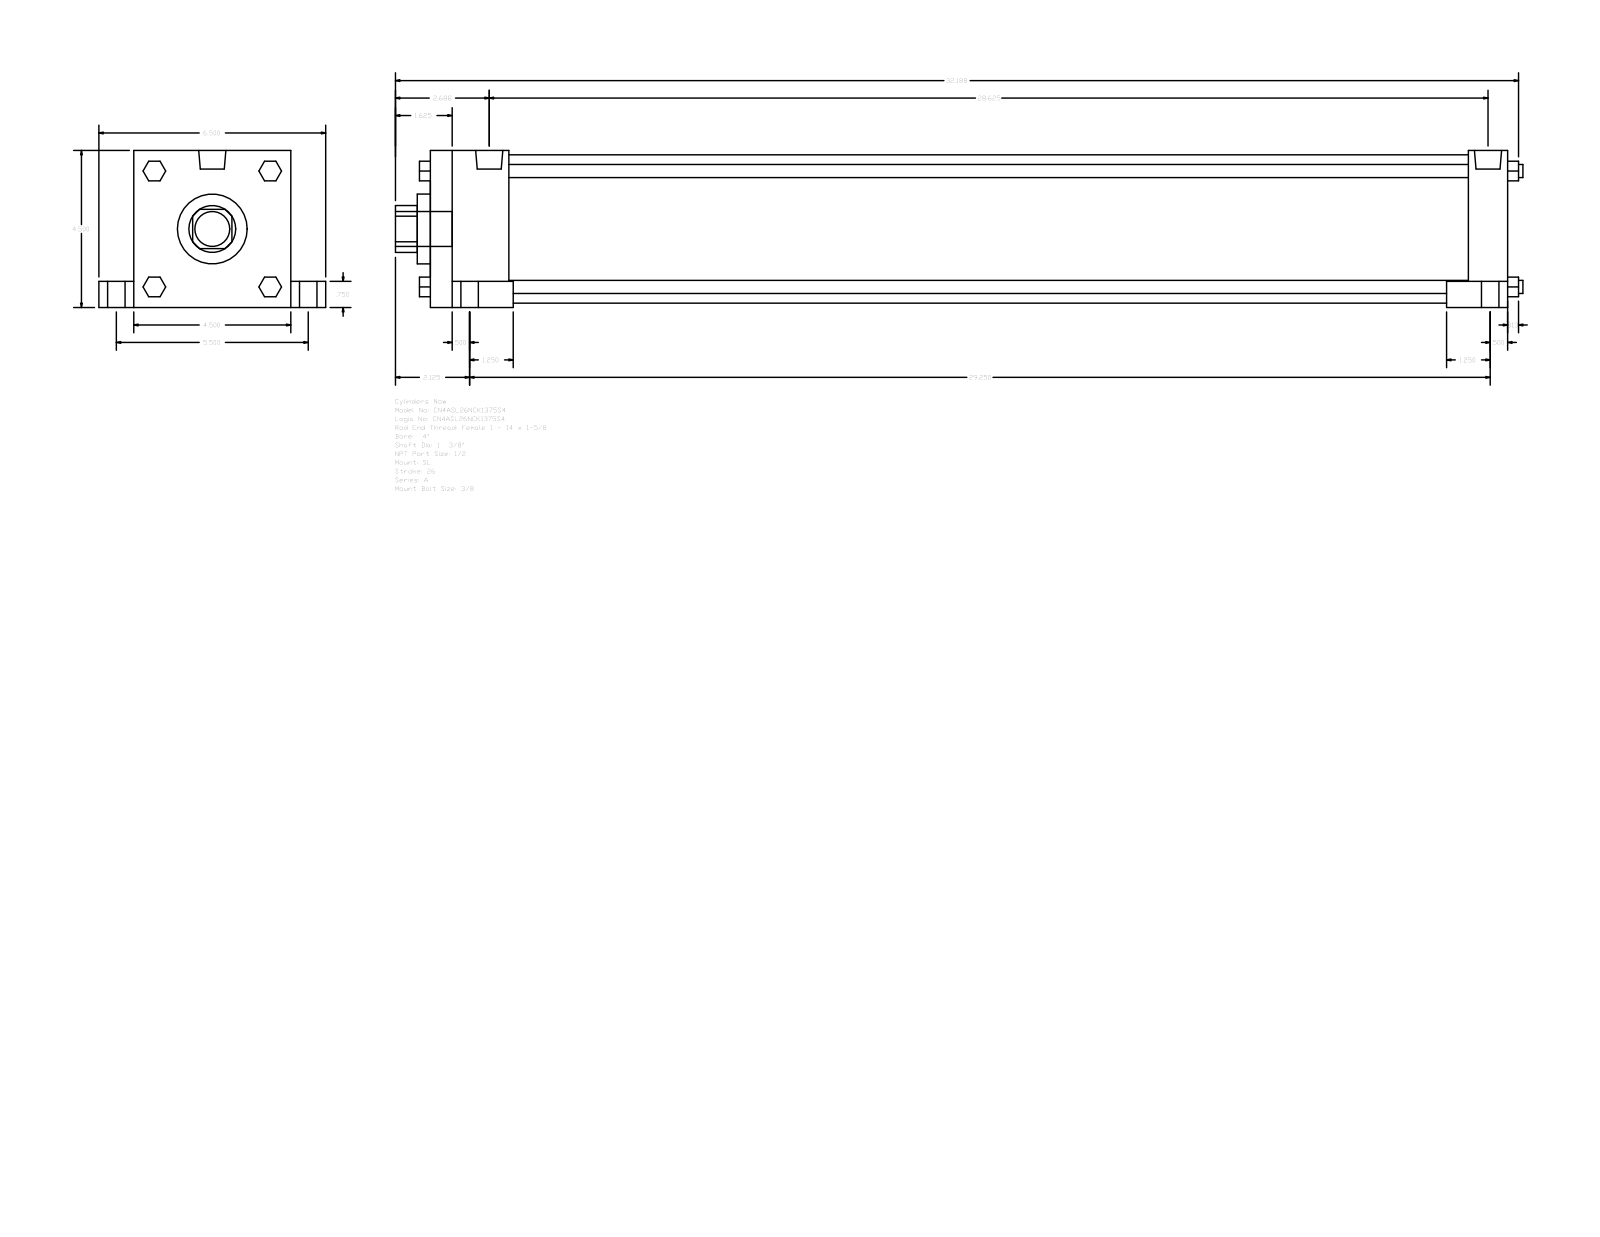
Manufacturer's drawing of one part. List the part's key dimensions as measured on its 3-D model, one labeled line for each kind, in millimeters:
Part name (STEP PRODUCT): A_SL__0400_1.375
STEP written by: GSSL Pune (CONFIG_CONTROL_DESIGN)
Units: millimetres
Bodies: 0 solids, 150 faces (114 planar, 36 cylindrical, 0 other)
Overall size (bounding box): 820.74 × 165.1 × 114.3
Round holes (diameter × count): ⌀34.92 ×1, ⌀50.8 ×1, ⌀107.95 ×1
Round bosses / shafts (diameter × count): ⌀19.05 ×4, ⌀12.7 ×4, ⌀9.53 ×4, ⌀8.73 ×4, ⌀19.77 ×2, ⌀25.4 ×1
Partial cylindrical surfaces — rounded edges, fillets, slot ends (radius × count): R17.06 ×1
Main face-to-face distances: 114.3, 784.22, 28.57, 25.4, 57.15, 727.07, 755.65, 698.5, 139.7, 19.05
